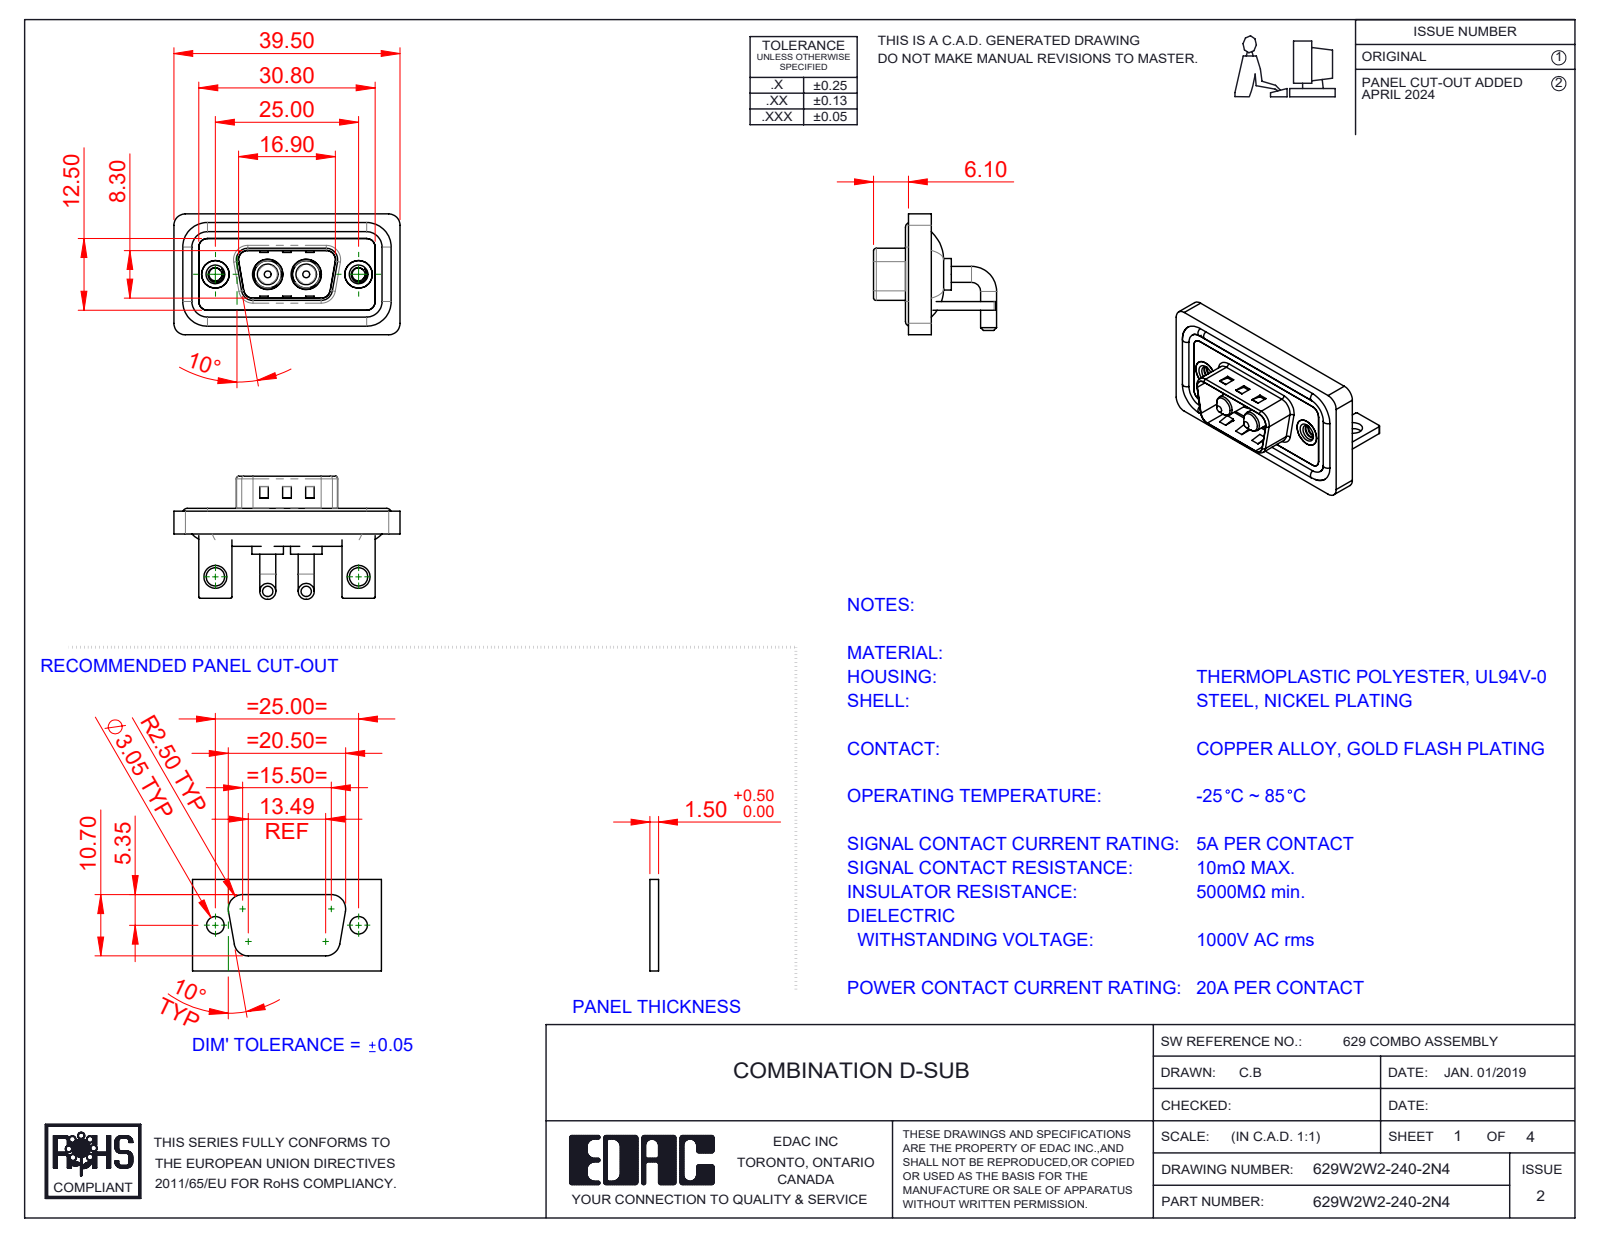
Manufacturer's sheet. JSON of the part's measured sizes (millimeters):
{"part_name": "629Combo Housing_2W2; 629Combo Shell Rear_09 Contacts; 629Combo Shell Front_09 Contacts; Power Pin_20A RA (+4 more)", "step_written_by": "SolidWorks 2023 (CONFIG_CONTROL_DESIGN)", "units": "millimeters", "bodies": {"solids": 13, "faces": 537, "planar": 185, "cylindrical": 240, "other": 112}, "overall_size": [39.5, 21.5, 21.1], "volume_mm3": 4862, "surface_area_mm2": 7754, "round_holes": [[2.26, 2], [3.2, 2], [4, 2], [4.8, 2], [4.85, 2], [5, 2], [5.3, 2]], "round_bosses_or_shafts": [[2.8, 4], [1.6, 4], [5.5, 2], [5.2, 2], [4.9, 2], [4.75, 2], [3.75, 2], [3.6, 2]], "partial_cylinders_radius": [[2, 19], [1.5, 18], [0.25, 16], [0.5, 9], [1.6, 8], [0.6, 4], [0.65, 4], [0.9, 4]], "face_to_face_distances": [0.4, 1.5, 2.9, 0.8, 1.1, 1.2, 2.1, 1.6, 3.7, 2.5], "hole_center_spacings": [9.14, 15.86, 25, 6.72]}
